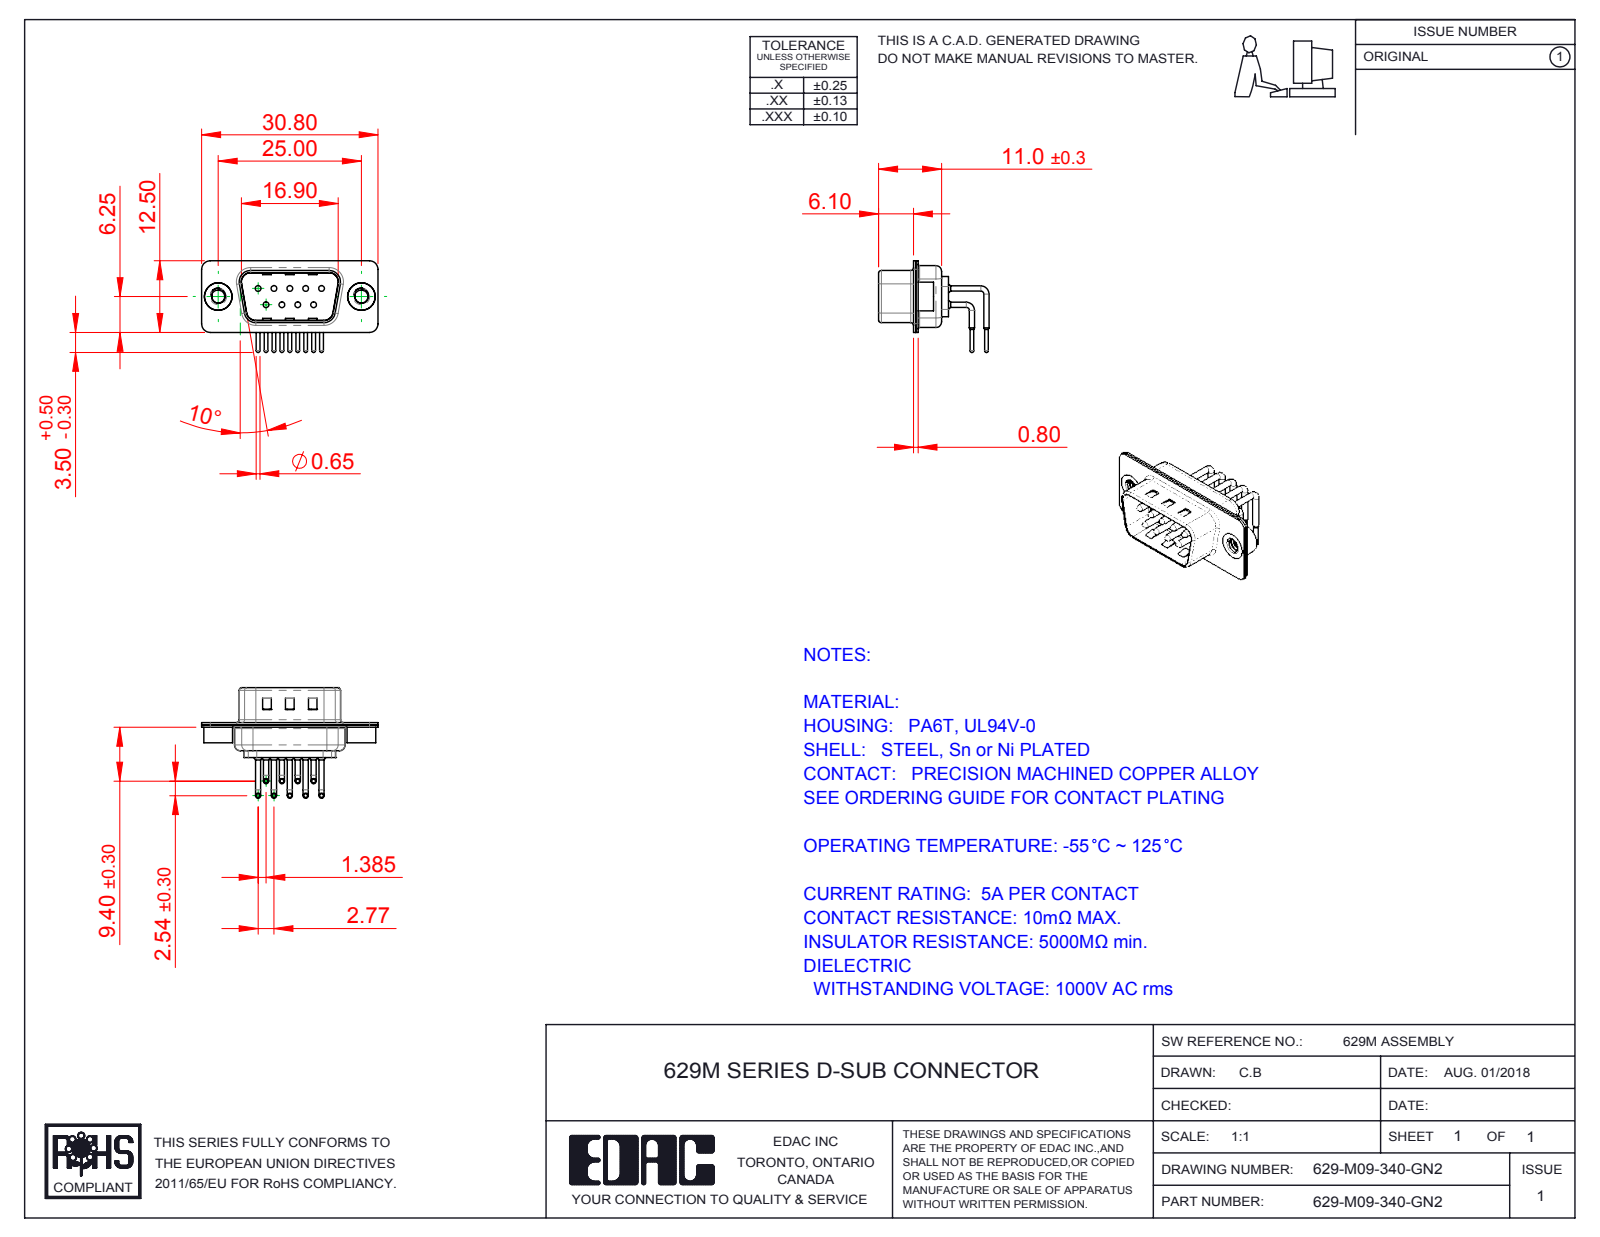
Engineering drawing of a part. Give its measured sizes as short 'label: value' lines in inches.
name: 629M Shell Rear_09 Contacts; 629M Shell Front_09 Contacts; 629M Housing_09 Contacts; 629-M09-340-GN2 (+3 more)
written by: SolidWorks 2016 (CONFIG_CONTROL_DESIGN)
unit: in
bodies: 14 solids, 1294 faces (683 planar, 453 cylindrical, 158 other)
size: 1.213 × 0.759 × 0.63
volume: 0.084 in³; area: 6.064 in²
holes: 9× ⌀0.039, 9× ⌀0.067, 9× ⌀0.079, 2× ⌀0.089, 2× ⌀0.157, 2× ⌀0.189
bosses: 18× ⌀0.035, 9× ⌀0.059, 9× ⌀0.026, 2× ⌀0.197, 2× ⌀0.193
rounds: 16× R0.059, 12× R0.079, 9× R0.04, 8× R0.02, 8× R0.063, 4× R0.01, 4× R0.024, 4× R0.026
face distances: 0.016, 0.033, 0.031, 0.376, 0.049, 0.409, 0.343, 0.014, 0.24, 0.224
hole spacings: 0.124, 0.109, 0.218, 0.198, 0.198, 0.327, 0.28, 0.294
